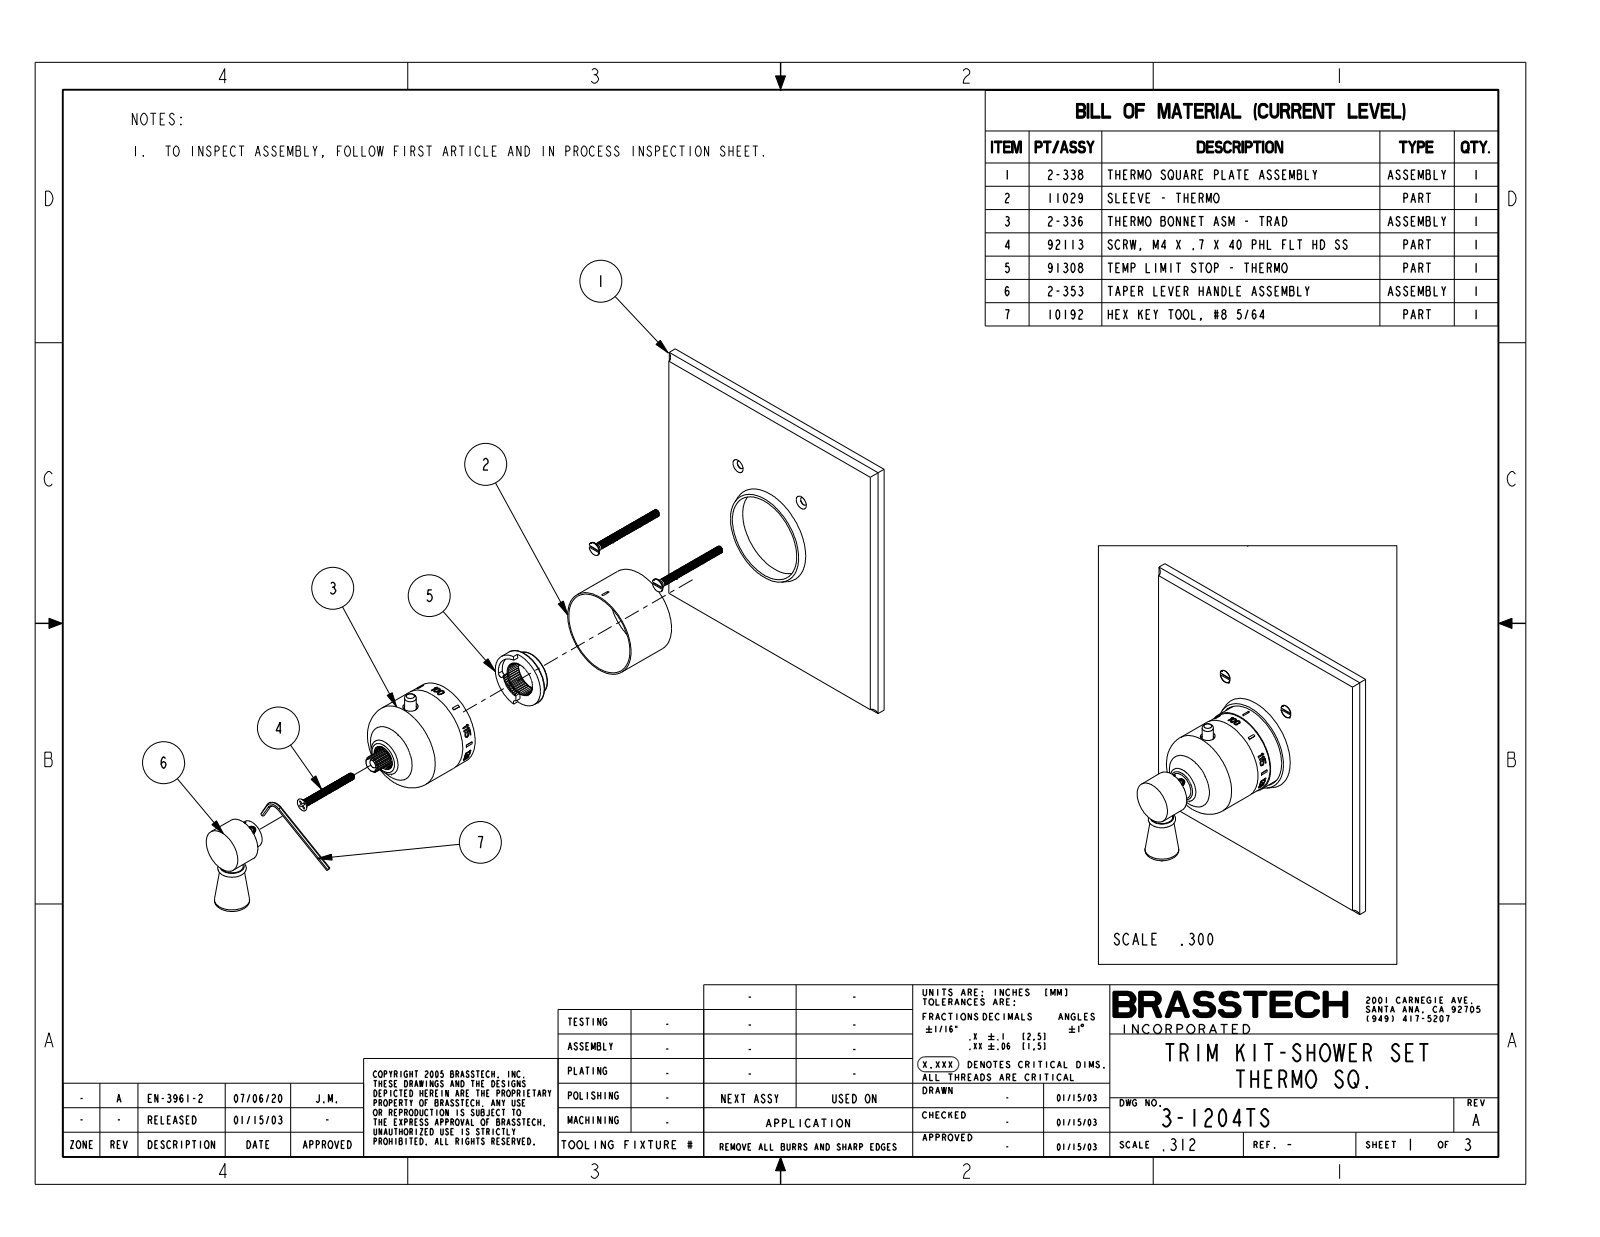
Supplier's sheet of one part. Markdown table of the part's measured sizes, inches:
| quantity | value |
| --- | --- |
| part name | 3-1204TS |
| STEP written by | CREO PARAMETRIC BY PTC INC, 2018400 (CONFIG_CONTROL_DESIGN) |
| units | inches |
| bodies | 1 solid, 402 faces (335 planar, 43 cylindrical, 24 other) |
| overall size | 6.5 × 6.5 × 3.739 |
| volume | 20.28 in³ |
| surface area | 110.6 in² |
| round holes (diameter × count) | 0.385 × 1 |
| round bosses / shafts (diameter × count) | 1.97 × 1, 1.94 × 1, 1.929 × 1, 0.98 × 1, 0.625 × 1, 0.37 × 1, 0.365 × 1, 0.26 × 1 |
| partial cylindrical surfaces (radius × count) | 0.125 × 4, 0.969 × 1 |
| main face-to-face distances | 0.313, 6.5, 3.031, 2.719, 2.706, 2.393, 0.326, 0.016, 2.721, 2.408 |
